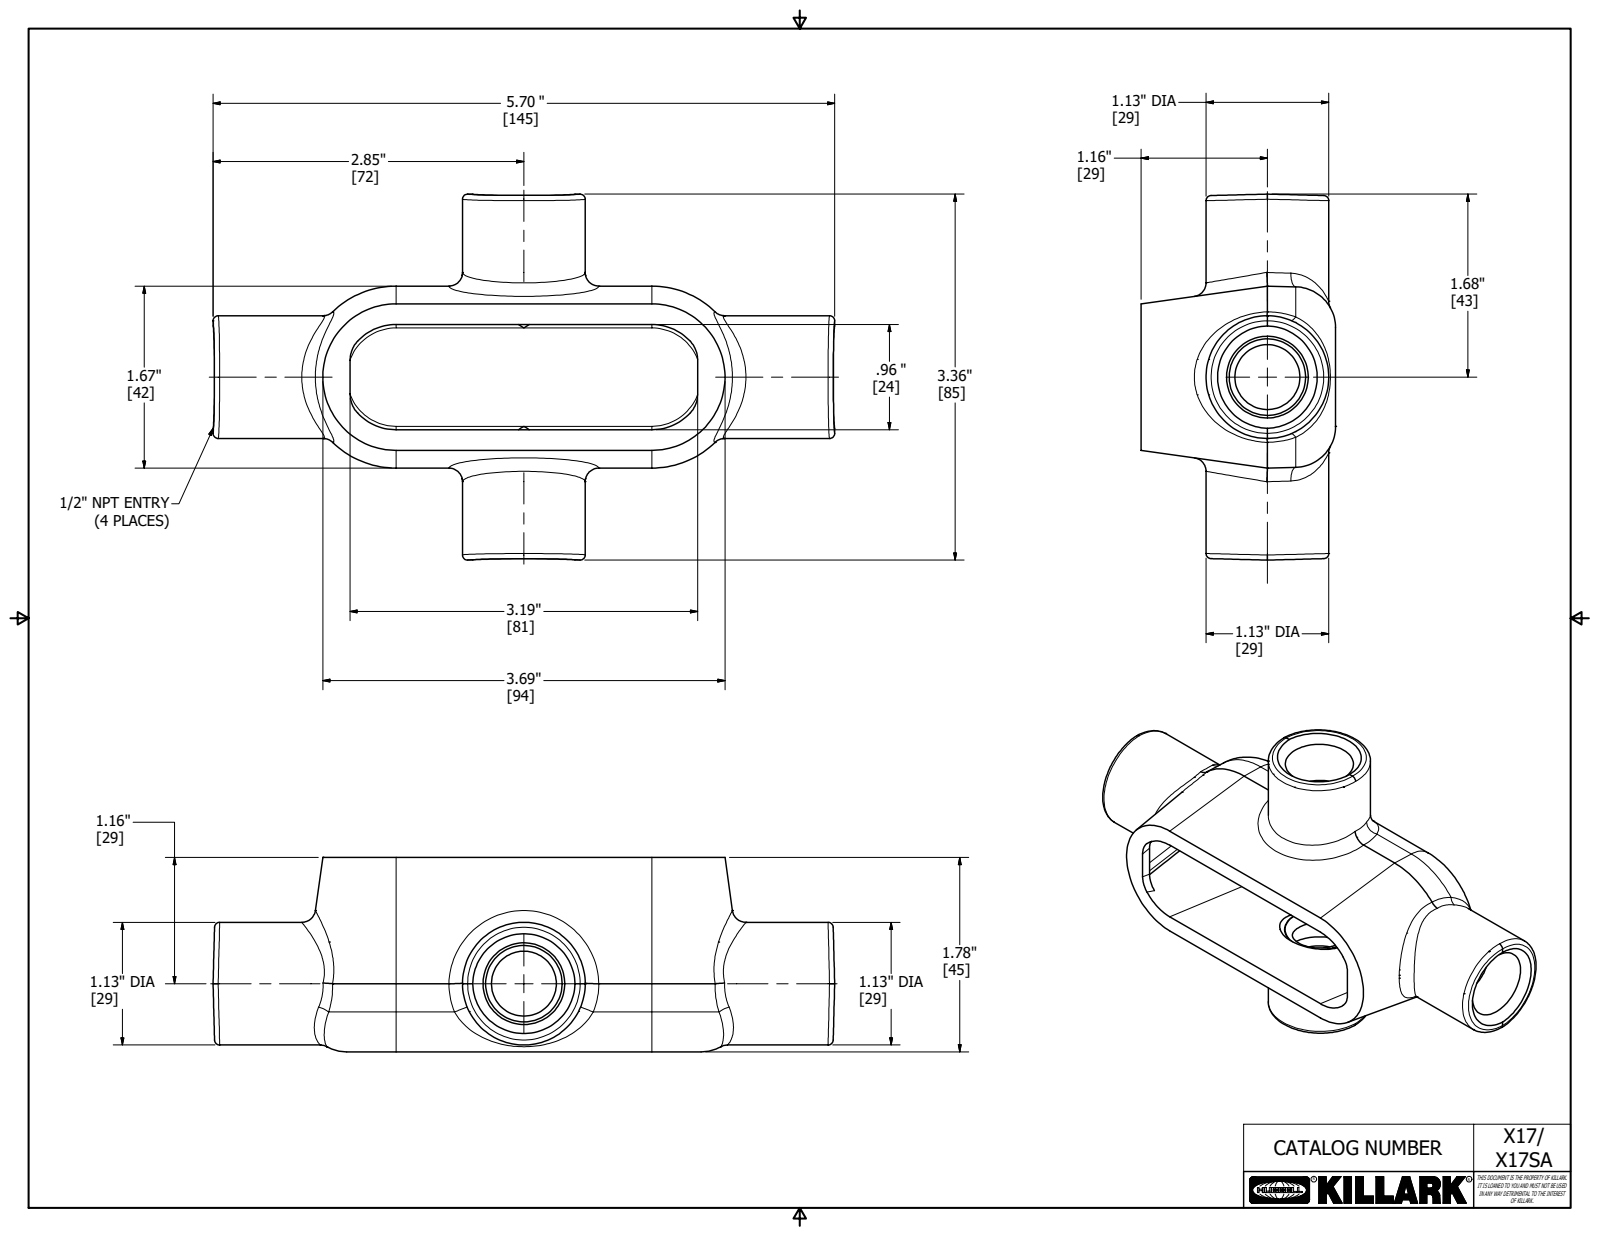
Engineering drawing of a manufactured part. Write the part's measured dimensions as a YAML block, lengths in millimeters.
part_name: "17648"
step_written_by: "Autodesk Inventor 2018 (AUTOMOTIVE_DESIGN)"
units: millimeters
bodies: {solids: 1, faces: 146, planar: 46, cylindrical: 28, other: 72}
overall_size: [144.8, 85.2, 45.3]
volume: 85200
surface_area: 39030
round_holes:
  - {diameter: 21.4, count: 2}
  - {diameter: 22.2, count: 1}
round_bosses_or_shafts:
  - {diameter: 28.6, count: 2}
partial_cylinders:
  - {radius: 1.3, count: 4}
  - {radius: 3.2, count: 4}
  - {radius: 4.7, count: 2}
  - {radius: 9.5, count: 2}
  - {radius: 11.1, count: 1}
face_to_face_distances: [4.7, 4.8, 45.3, 40.5, 4, 4.8, 0.8, 44.5, 144.8, 21.4]
